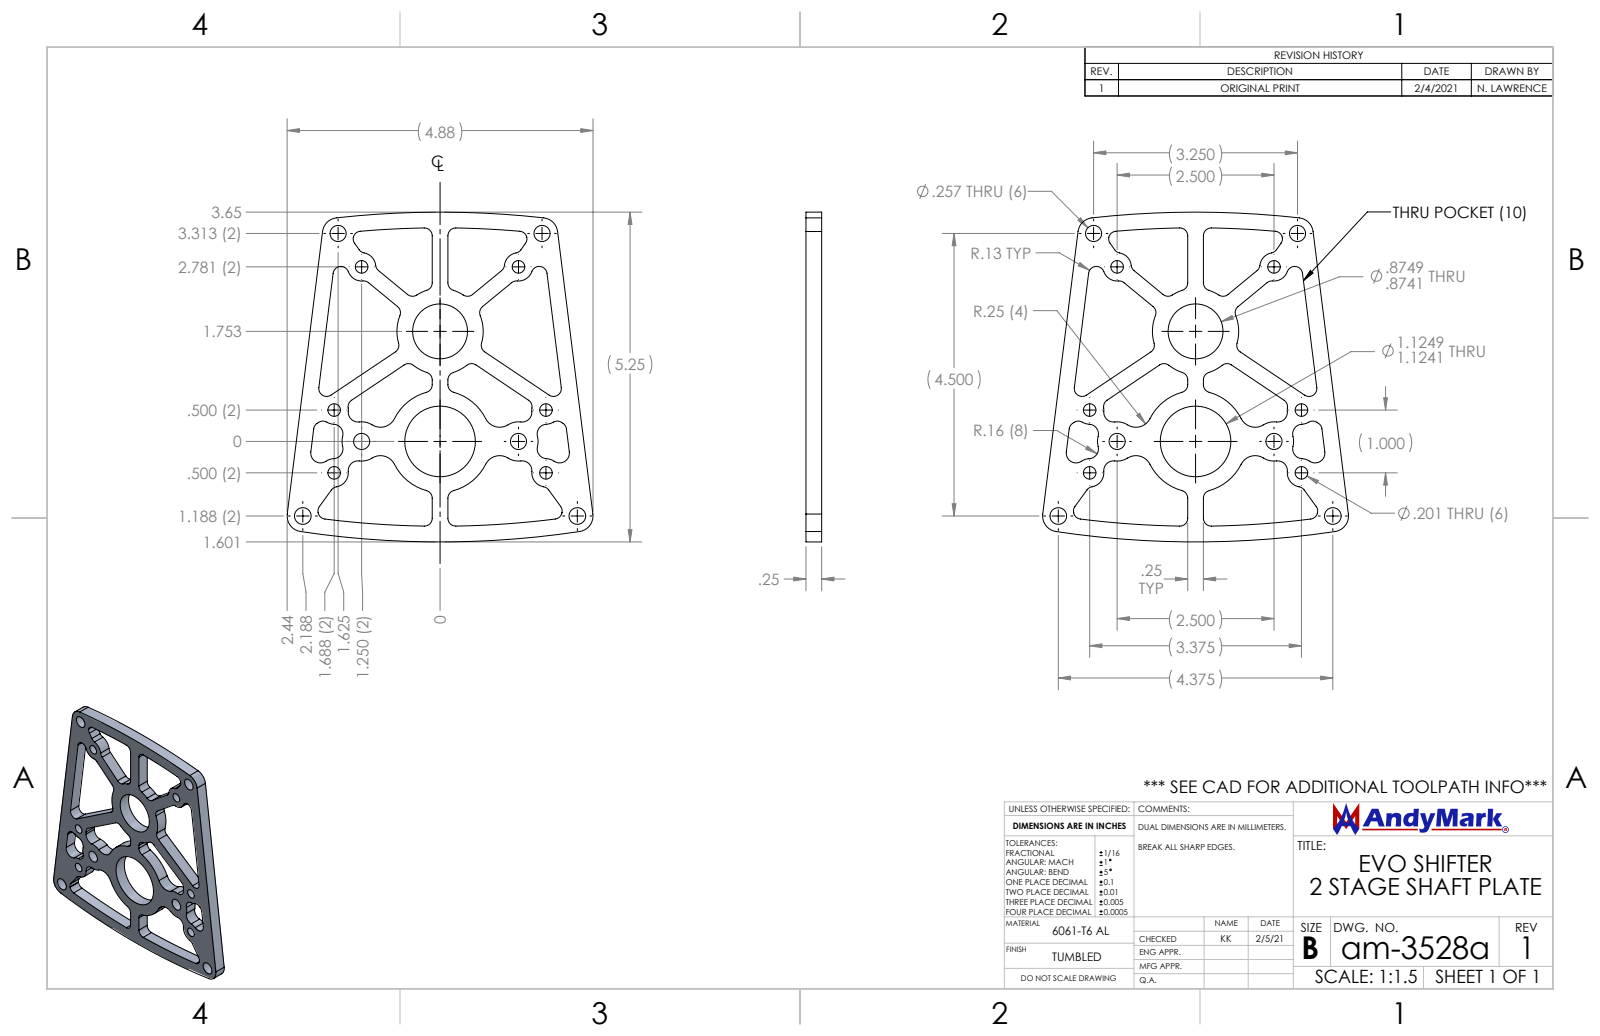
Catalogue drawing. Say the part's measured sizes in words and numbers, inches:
The part is named "am-3528a Evo 2 Stage Shaft Plate". Its 3-D file was written by "SolidWorks 2019 (AUTOMOTIVE_DESIGN)". It is 1 solid with 142 faces: 28 planar, 114 cylindrical and 0 other. Overall it measures 5.253 by 4.875 by 0.25 inches. Its volume is 2.517 cubic inches and its surface area 38.36 square inches. Round holes: 6 of diameter 0.201, 4 of diameter 0.257, 2 of diameter 0.266, 1 of diameter 0.875, 1 of diameter 1.125. Partial cylindrical surfaces (rounded edges, fillets, slot ends): 46 of radius 0.125, 10 of radius 0.156, 8 of radius 0.25, 6 of radius 0.226, 2 of radius 0.313, 2 of radius 14.75, 2 of radius 15, 1 of radius 0.687. The main face-to-face distances are 0.25, 0.25. The hole center spacings are 1.76, 0.664, 2.98, 0.651, 0.85, 1, 1.25, 1.513.
